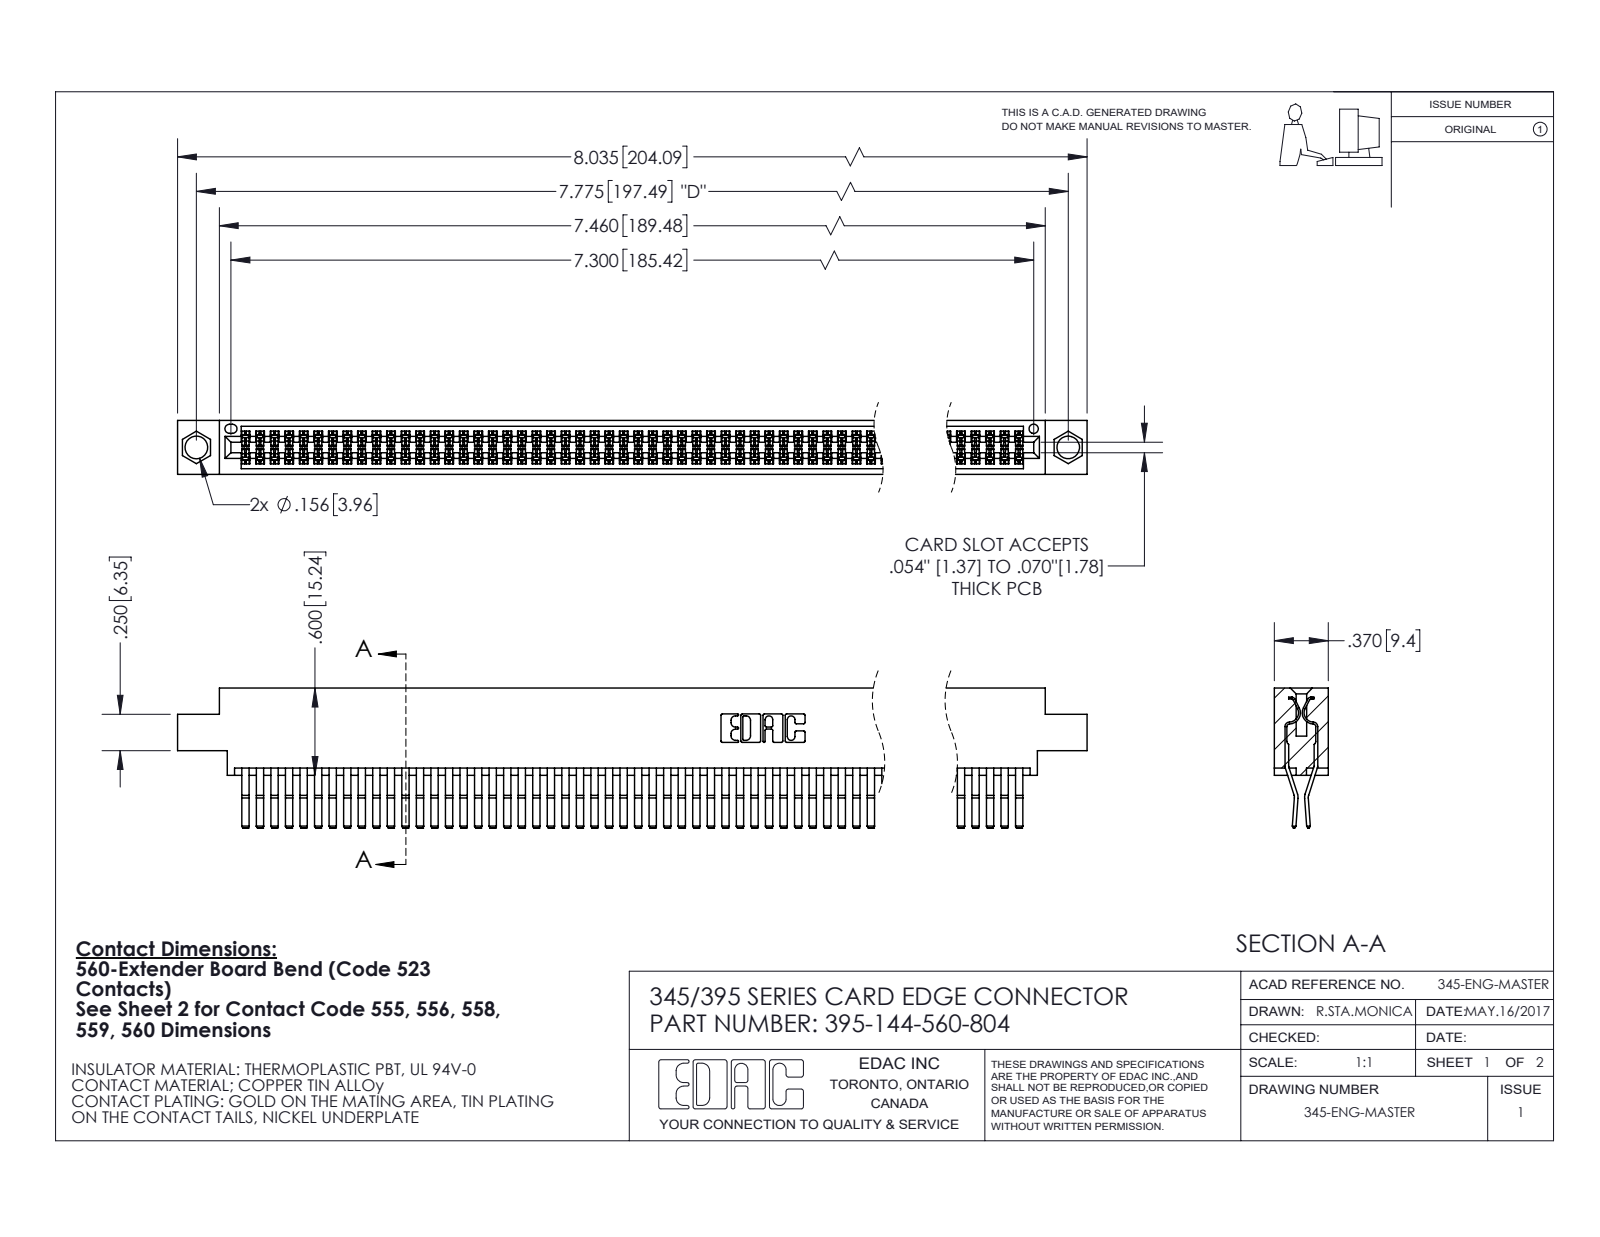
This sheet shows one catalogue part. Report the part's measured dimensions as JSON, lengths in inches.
{"part_name": "345-292-001_560 Tail; 345 Part_0.170 Offset - 0.156 Dia-TI; 395-144-560-804", "step_written_by": "SolidWorks 2020 (CONFIG_CONTROL_DESIGN)", "units": "inches", "bodies": {"solids": 145, "faces": 7632, "planar": 4850, "cylindrical": 2782, "other": 0}, "overall_size": [8.035, 0.962, 0.37], "volume_in3": 1.271, "surface_area_in2": 52.38, "round_holes": [[0.156, 2], [0.064, 1]], "partial_cylinders_radius": [[0.006, 216], [0.01, 22], [0.007, 6], [0.031, 6], [0.026, 3], [0.01, 2], [0.014, 2], [0.019, 2]], "face_to_face_distances": [0.025, 0.072, 0.298, 0.37, 0.2, 0.098, 0.272, 0.225, 0.175, 0.149], "hole_center_spacings": [0.27, 7.539, 7.775]}
